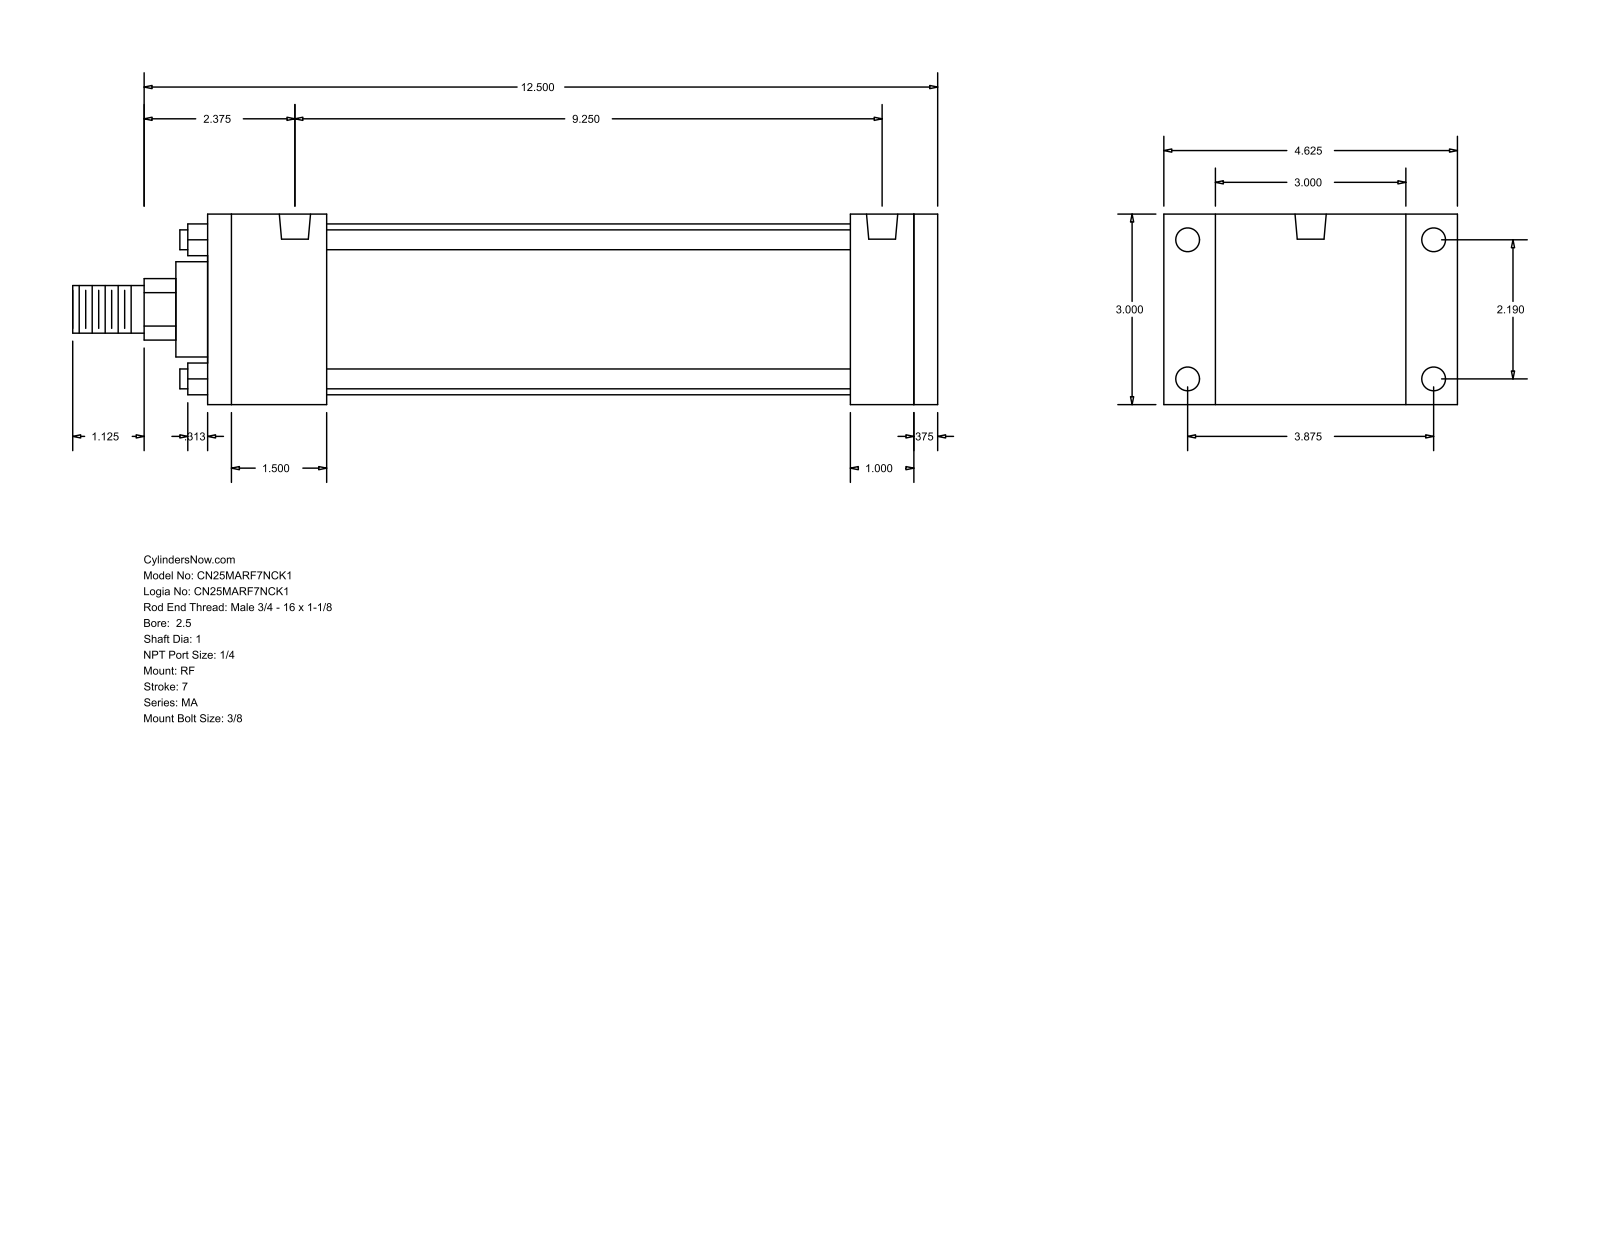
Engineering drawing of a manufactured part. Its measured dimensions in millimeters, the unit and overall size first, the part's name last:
Units: millimetres
Overall size (bounding box): 346.07 × 117.47 × 76.2
Round holes (diameter × count): ⌀7.94 ×4, ⌀9.53 ×4, ⌀12.49 ×2
Round bosses / shafts (diameter × count): ⌀7.94 ×4, ⌀68.33 ×1, ⌀38.1 ×1, ⌀25.4 ×1, ⌀19.05 ×1
Partial cylindrical surfaces — rounded edges, fillets, slot ends (radius × count): R12.29 ×1
Main face-to-face distances: 76.2, 292.1, 282.58, 9.52, 47.63, 257.17, 209.54, 234.95, 244.47, 25.41
Hole centre spacings: 55.62, 98.42, 113.05, 234.94
Bodies: 0 solids, 92 faces (64 planar, 28 cylindrical, 0 other)
Part name (STEP PRODUCT): MA_RF__0250_1
STEP written by: GSSL Pune (CONFIG_CONTROL_DESIGN)
